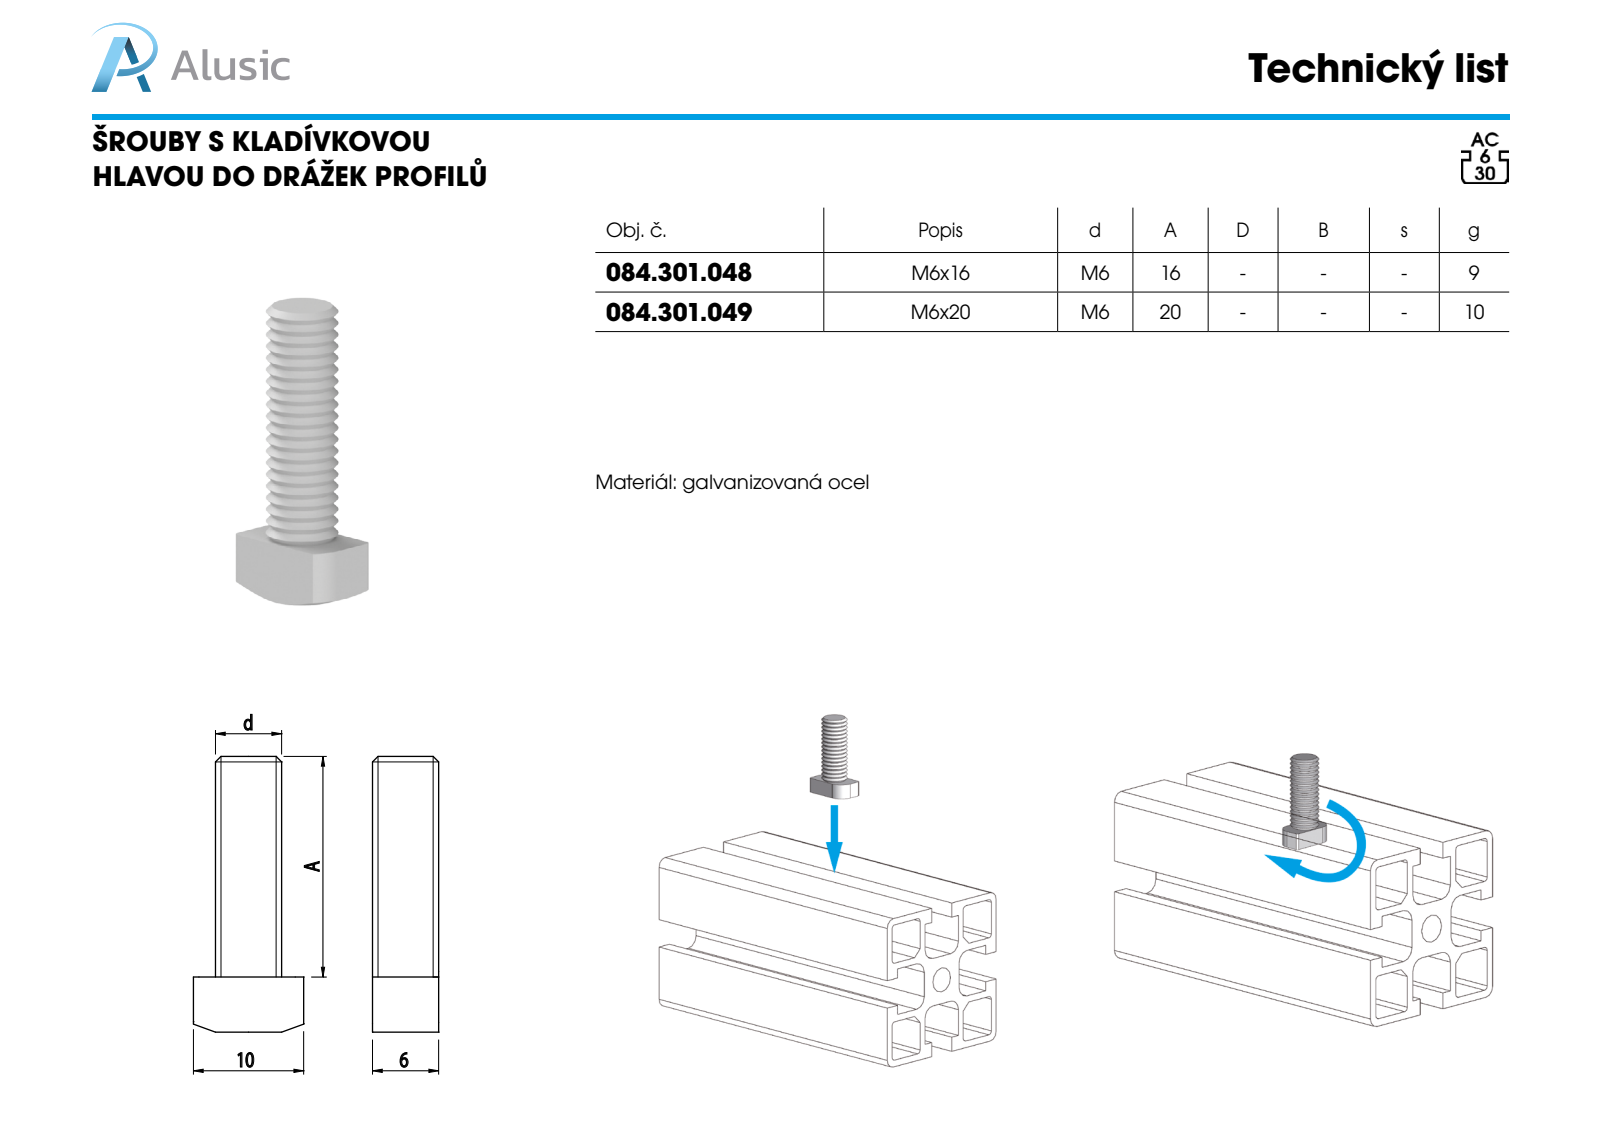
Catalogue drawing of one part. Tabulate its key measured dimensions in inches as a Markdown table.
| quantity | value |
| --- | --- |
| part name | 084.301.049 |
| STEP written by | SolidWorks 2012 (CONFIG_CONTROL_DESIGN) |
| units | inches |
| bodies | 1 solid, 93 faces (7 planar, 4 cylindrical, 82 other) |
| overall size | 0.984 × 0.394 × 0.236 |
| volume | 0.046 in³ |
| surface area | 1.15 in² |
| partial cylindrical surfaces (radius × count) | 0.02 × 2, 0.118 × 2 |
| main face-to-face distances | 0.236, 0.197, 0.984, 0.787, 0.394 |
